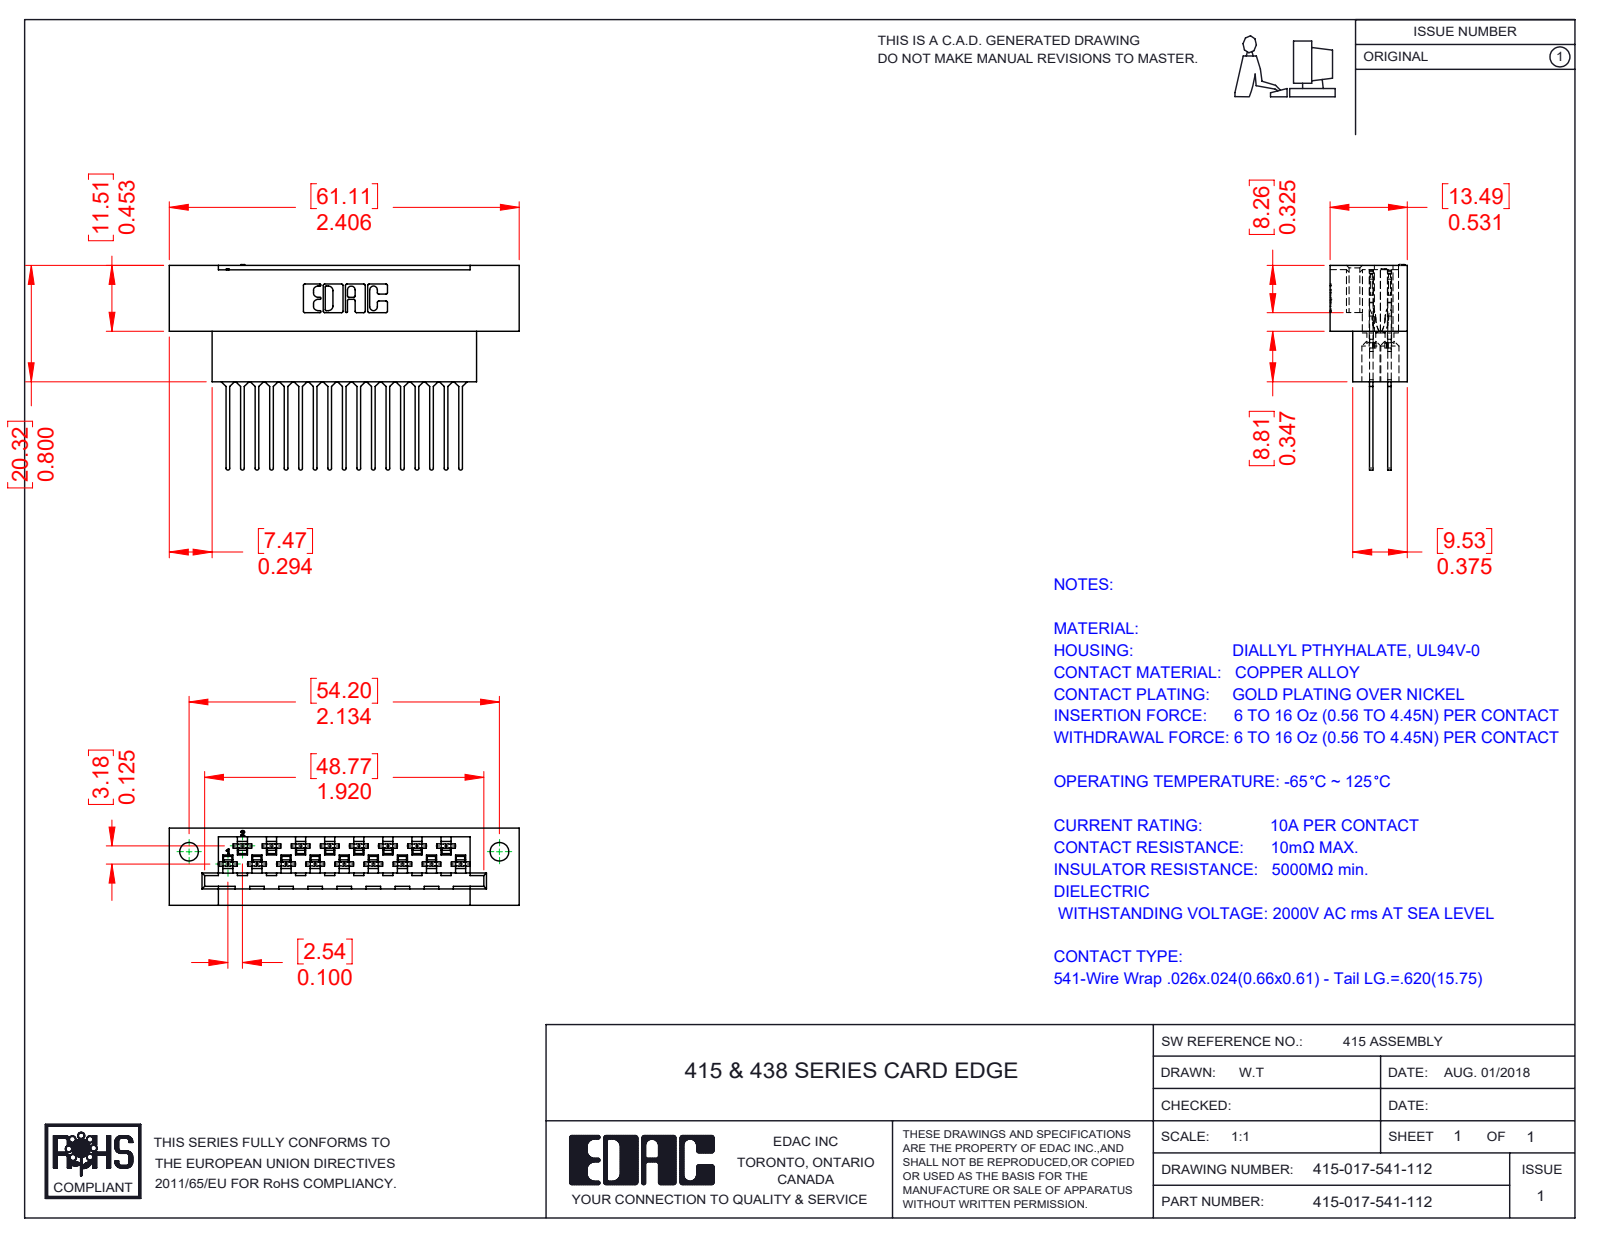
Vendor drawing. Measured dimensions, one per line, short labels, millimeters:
name: 415-210-001_415-210-017-112; 516-290-001_541; 415-017-541-112
written by: SolidWorks 2016 (CONFIG_CONTROL_DESIGN)
unit: mm
bodies: 18 solids, 1810 faces (1149 planar, 486 cylindrical, 175 other)
size: 61.11 × 35.85 × 13.49
volume: 10 219 mm³; area: 12 120 mm²
holes: 17× ⌀1.27, 17× ⌀3.3, 2× ⌀3.25
rounds: 68× R0.3, 68× R0.56, 34× R0.18, 34× R0.2, 34× R0.41, 34× R2.03, 22× R0.25, 17× R0.33
face distances: 3.18, 0.61, 13.49, 1.88, 7.49, 1.27, 20.32, 6.61, 6.88, 6
hole spacings: 5.08, 10.16, 15.24, 20.32, 2.54, 4.06, 7.62, 8.25
